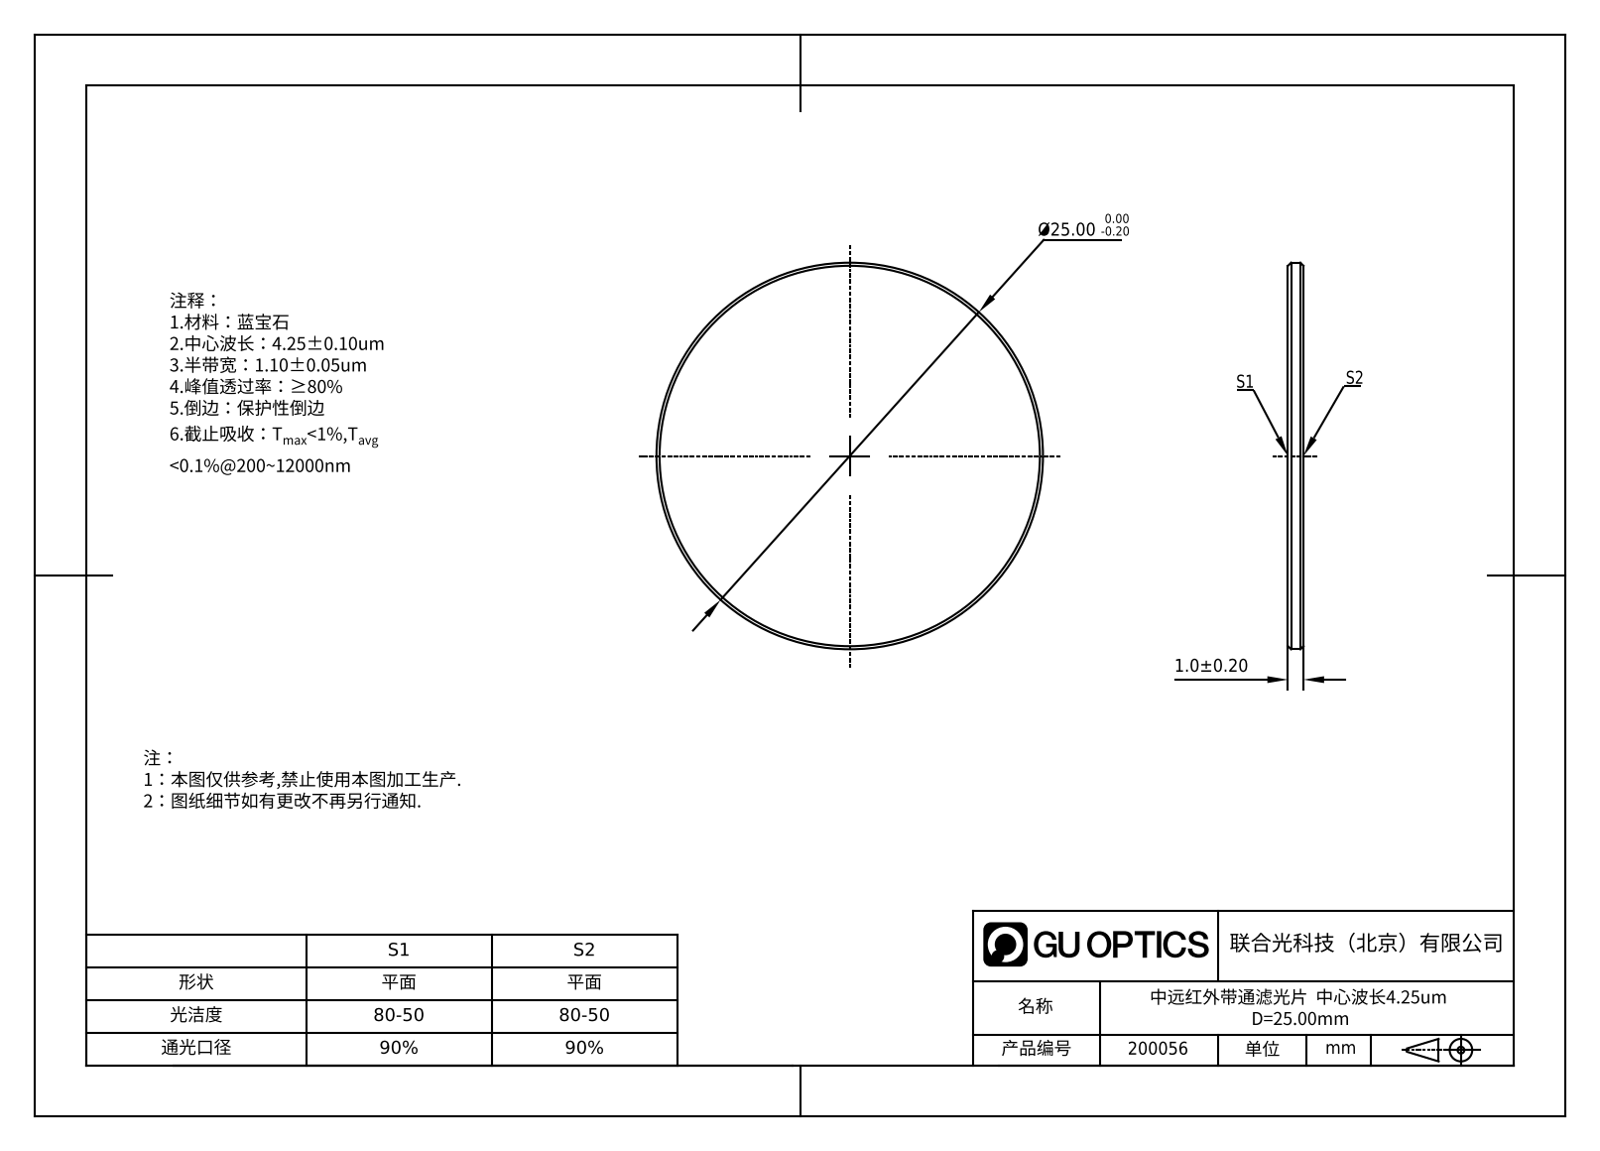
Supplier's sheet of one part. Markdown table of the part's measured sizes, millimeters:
| quantity | value |
| --- | --- |
| part name | GNIF-1100-4250-D25 |
| STEP written by | SolidWorks 2022 (AUTOMOTIVE_DESIGN) |
| units | millimeters |
| bodies | 1 solid, 8 faces (2 planar, 2 cylindrical, 4 other) |
| overall size | 25 × 25 × 1 |
| volume | 488 mm³ |
| surface area | 1 042 mm² |
| round bosses / shafts (diameter × count) | 25 × 1 |
| main face-to-face distances | 1 |
